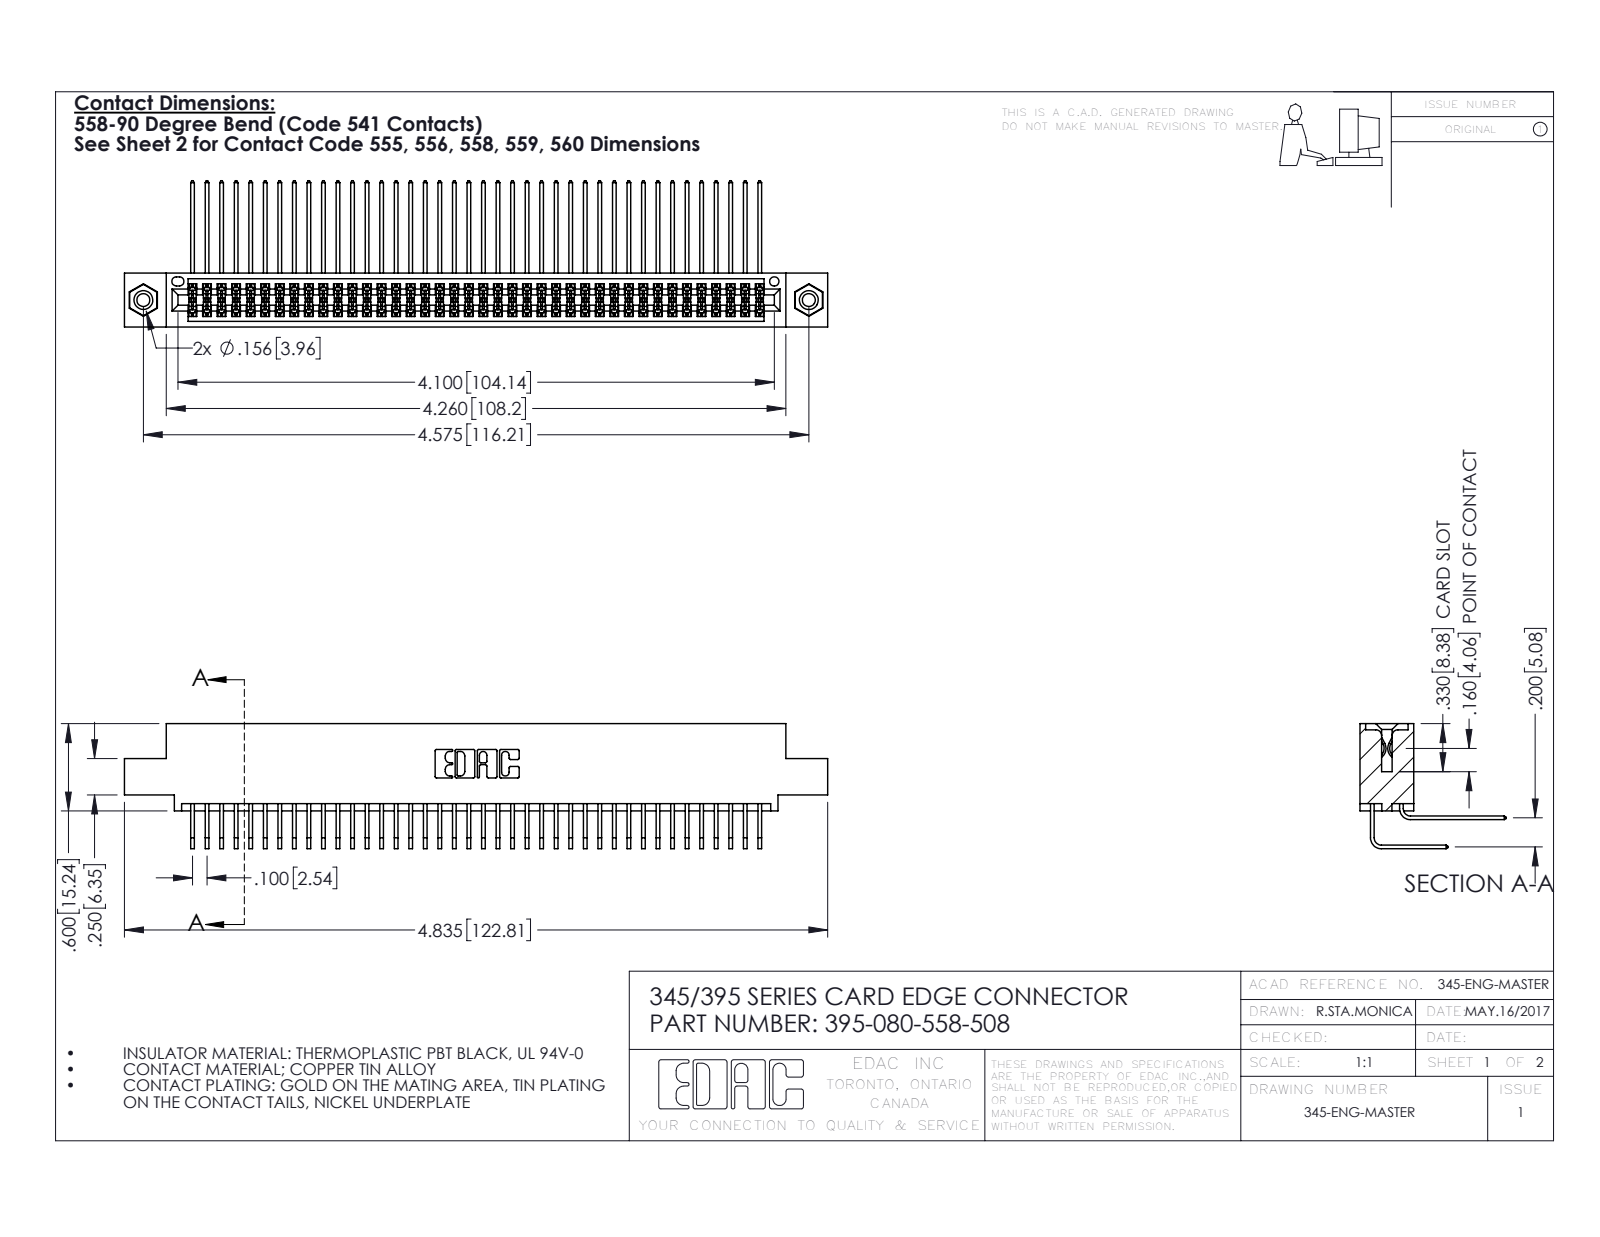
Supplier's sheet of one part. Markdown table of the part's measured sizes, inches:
| quantity | value |
| --- | --- |
| part name | 345-292-001_558 559 Tail - 1; 395-080-558-508; 345 Part_0.110 Offset - 0.156 Dia-TI; 345-250-001_345-250-003-102 (+1 more) |
| STEP written by | SolidWorks 2016 (CONFIG_CONTROL_DESIGN) |
| units | inches |
| bodies | 83 solids, 4350 faces (2916 planar, 1418 cylindrical, 16 other) |
| overall size | 4.835 × 1.005 × 0.859 |
| volume | 0.75 in³ |
| surface area | 31.63 in² |
| round holes (diameter × count) | 0.089 × 2, 0.125 × 2, 0.156 × 2, 0.064 × 1 |
| round bosses / shafts (diameter × count) | 0.155 × 2 |
| partial cylindrical surfaces (radius × count) | 0.006 × 121, 0.01 × 22, 0.007 × 6, 0.031 × 6, 0.026 × 3, 0.014 × 2, 0.019 × 2, 0.022 × 2 |
| main face-to-face distances | 0.072, 0.298, 0.2, 0.37, 0.098, 0.272, 0.025, 0.225, 0.025, 0.175 |
| hole center spacings | 0.27, 4.339, 4.575 |
